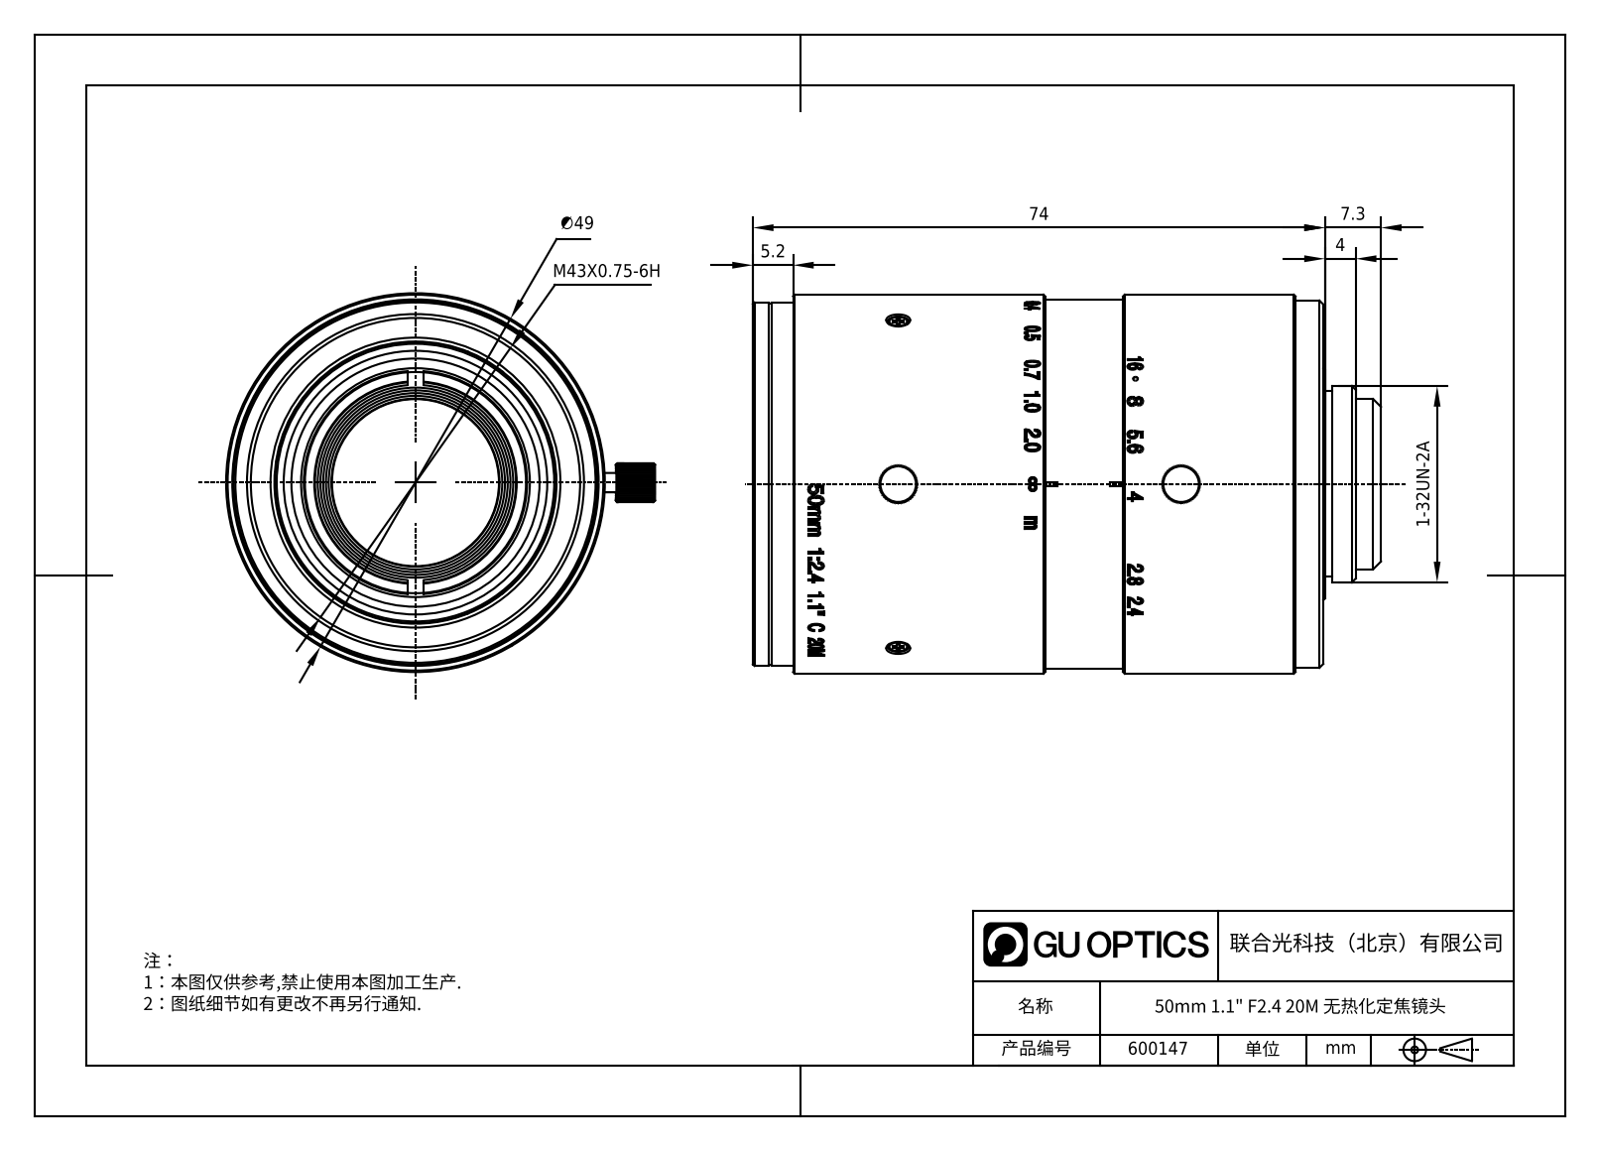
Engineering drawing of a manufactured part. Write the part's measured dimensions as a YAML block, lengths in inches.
part_name: "600147"
step_written_by: "SolidWorks 2020 (CONFIG_CONTROL_DESIGN)"
units: inches
bodies: {solids: 0, faces: 2825, planar: 867, cylindrical: 681, other: 1277}
overall_size: [3.199, 2.185, 1.929]
round_holes:
  - {diameter: 0.079, count: 8}
  - {diameter: 0.051, count: 6}
  - {diameter: 0.071, count: 6}
  - {diameter: 0.039, count: 5}
  - {diameter: 0.043, count: 4}
  - {diameter: 0.059, count: 3}
  - {diameter: 0.106, count: 3}
  - {diameter: 0.126, count: 3}
  - {diameter: 0.15, count: 3}
  - {diameter: 0.591, count: 1}
  - {diameter: 0.61, count: 1}
  - {diameter: 0.63, count: 1}
round_bosses_or_shafts:
  - {diameter: 0.098, count: 8}
  - {diameter: 0.067, count: 6}
  - {diameter: 0.055, count: 6}
  - {diameter: 0.197, count: 3}
  - {diameter: 0.193, count: 3}
  - {diameter: 0.122, count: 3}
  - {diameter: 0.11, count: 3}
  - {diameter: 0.106, count: 3}
partial_cylinders:
  - {radius: 0.005, count: 18}
  - {radius: 0.012, count: 18}
  - {radius: 0.059, count: 12}
  - {radius: 0.098, count: 8}
  - {radius: 0.02, count: 6}
  - {radius: 0.03, count: 6}
  - {radius: 0.053, count: 6}
  - {radius: 0.116, count: 6}
face_to_face_distances: [2.441, 0.248, 0.778, 0.327, 2.52, 0.086, 0.531, 2.768, 0.858, 1.909]
hole_center_spacings: [0.222, 0.368, 0.591, 0.669, 0.85, 1.159, 1.219, 1.441]
